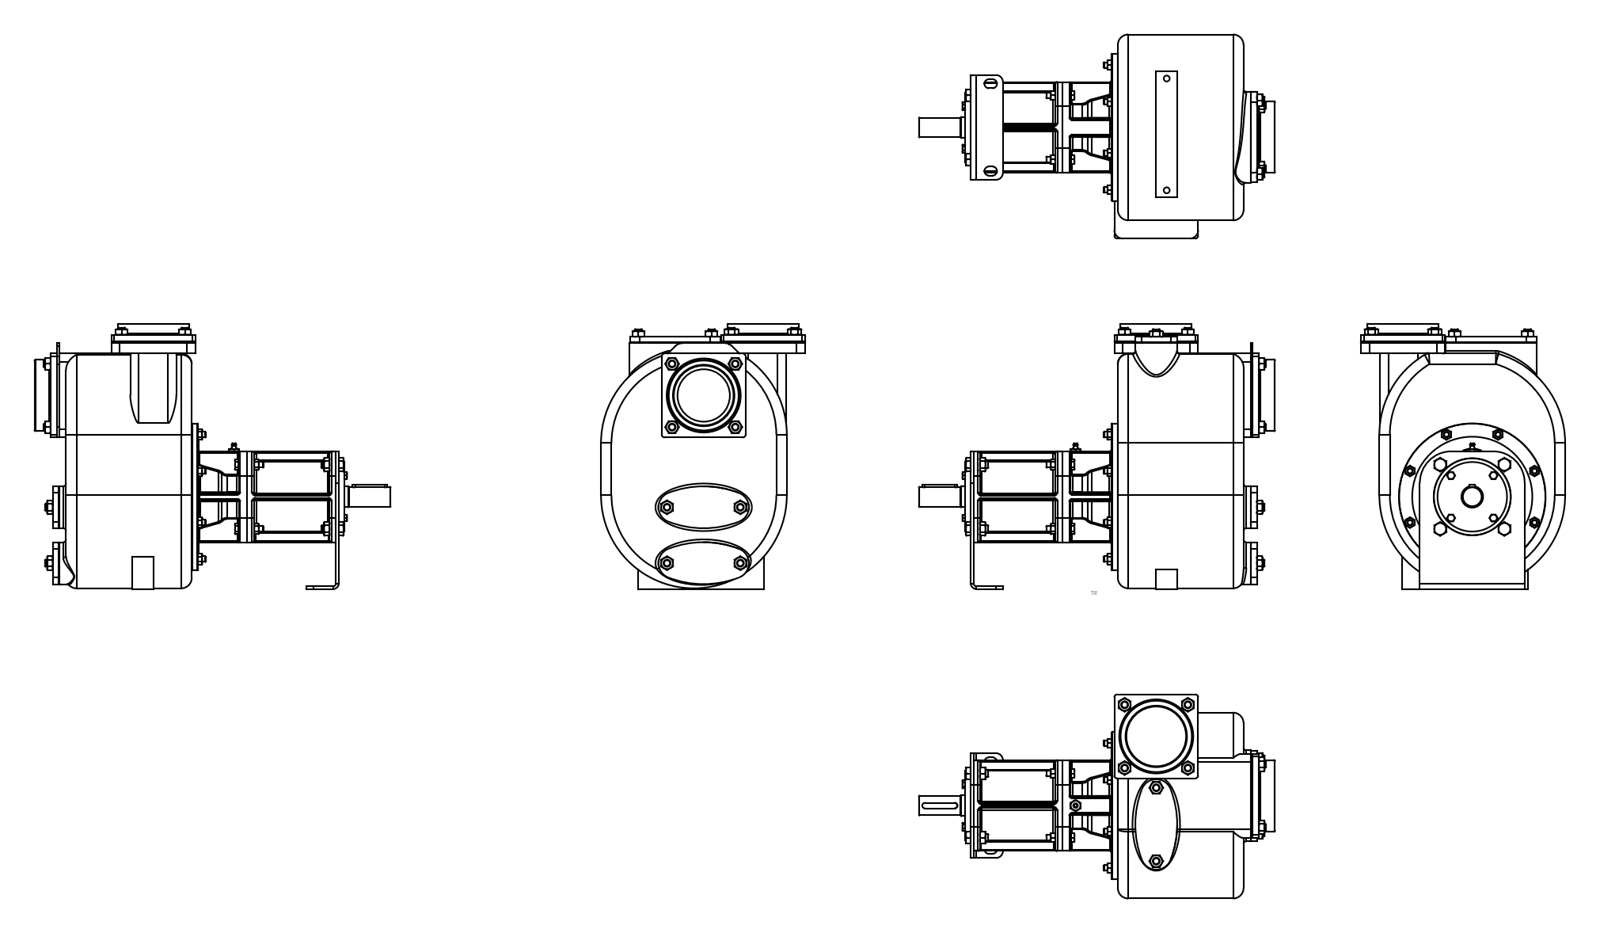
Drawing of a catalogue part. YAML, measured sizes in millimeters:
part_name: "S_83_B"
step_written_by: "CREO PARAMETRIC BY PTC INC, 2017110 (CONFIG_CONTROL_DESIGN)"
units: millimeters
bodies: {solids: 2, faces: 655, planar: 161, cylindrical: 294, other: 200}
overall_size: [509.5, 379, 292]
volume: 17210000
surface_area: 653908
round_holes:
  - {diameter: 11.5, count: 14}
  - {diameter: 10, count: 12}
  - {diameter: 11, count: 12}
  - {diameter: 7, count: 4}
  - {diameter: 8.5, count: 2}
  - {diameter: 85.5, count: 2}
  - {diameter: 31, count: 1}
  - {diameter: 63, count: 1}
  - {diameter: 75, count: 1}
  - {diameter: 90, count: 1}
round_bosses_or_shafts:
  - {diameter: 102, count: 2}
  - {diameter: 210, count: 1}
  - {diameter: 172, count: 1}
  - {diameter: 116.5, count: 1}
  - {diameter: 100, count: 1}
  - {diameter: 99.5, count: 1}
  - {diameter: 30, count: 1}
  - {diameter: 28, count: 1}
partial_cylinders:
  - {radius: 2, count: 54}
  - {radius: 3, count: 18}
  - {radius: 15, count: 15}
  - {radius: 4, count: 12}
  - {radius: 12, count: 12}
  - {radius: 140, count: 6}
  - {radius: 6.5, count: 4}
  - {radius: 22, count: 4}
face_to_face_distances: [1, 180, 9, 15, 8, 197, 210, 12, 9.5, 4]
hole_center_spacings: [44.12, 59.1, 63.99, 77.94, 89.36, 90.5, 93.47, 96.5]
